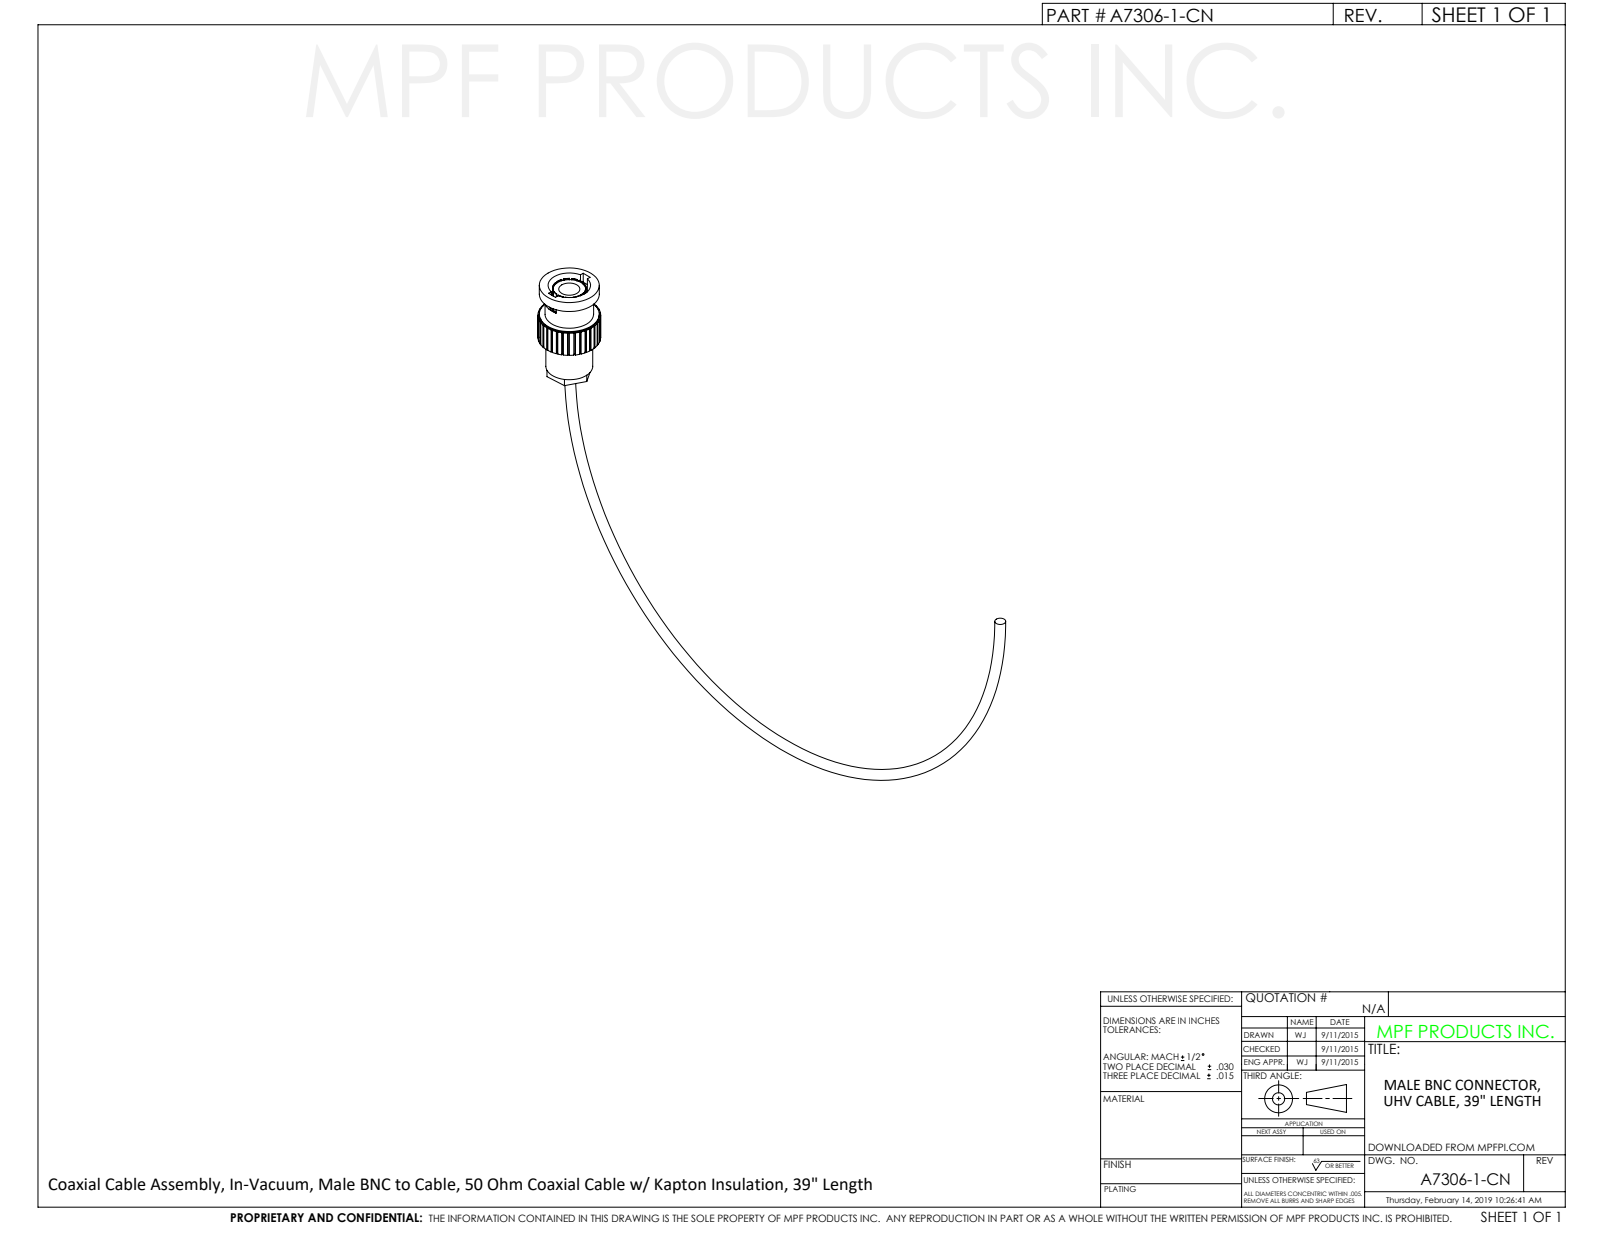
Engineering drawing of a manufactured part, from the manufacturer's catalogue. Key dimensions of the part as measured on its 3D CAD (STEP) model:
Part name (STEP PRODUCT): A7306-1-CN
STEP written by: SolidWorks 2012 (CONFIG_CONTROL_DESIGN)
Units: inches
Bodies: 2 solids, 308 faces (220 planar, 86 cylindrical, 2 other)
Overall size (bounding box): 5.924 × 3.816 × 0.575
Volume: 0.204 in³ · Surface area: 6.503 in²
Round holes (diameter × count): ⌀0.074 ×1, ⌀0.158 ×1, ⌀0.194 ×1, ⌀0.39 ×1
Round bosses / shafts (diameter × count): ⌀0.55 ×1, ⌀0.525 ×1, ⌀0.445 ×1, ⌀0.43 ×1, ⌀0.308 ×1
Partial cylindrical surfaces — rounded edges, fillets, slot ends (radius × count): R0.068 ×1, R0.15 ×1, R0.151 ×1, R0.287 ×1
Main face-to-face distances: 0.978, 0.014, 0.54, 0.653, 0.325, 0.878, 0.225, 0.1, 0.395, 0.385
